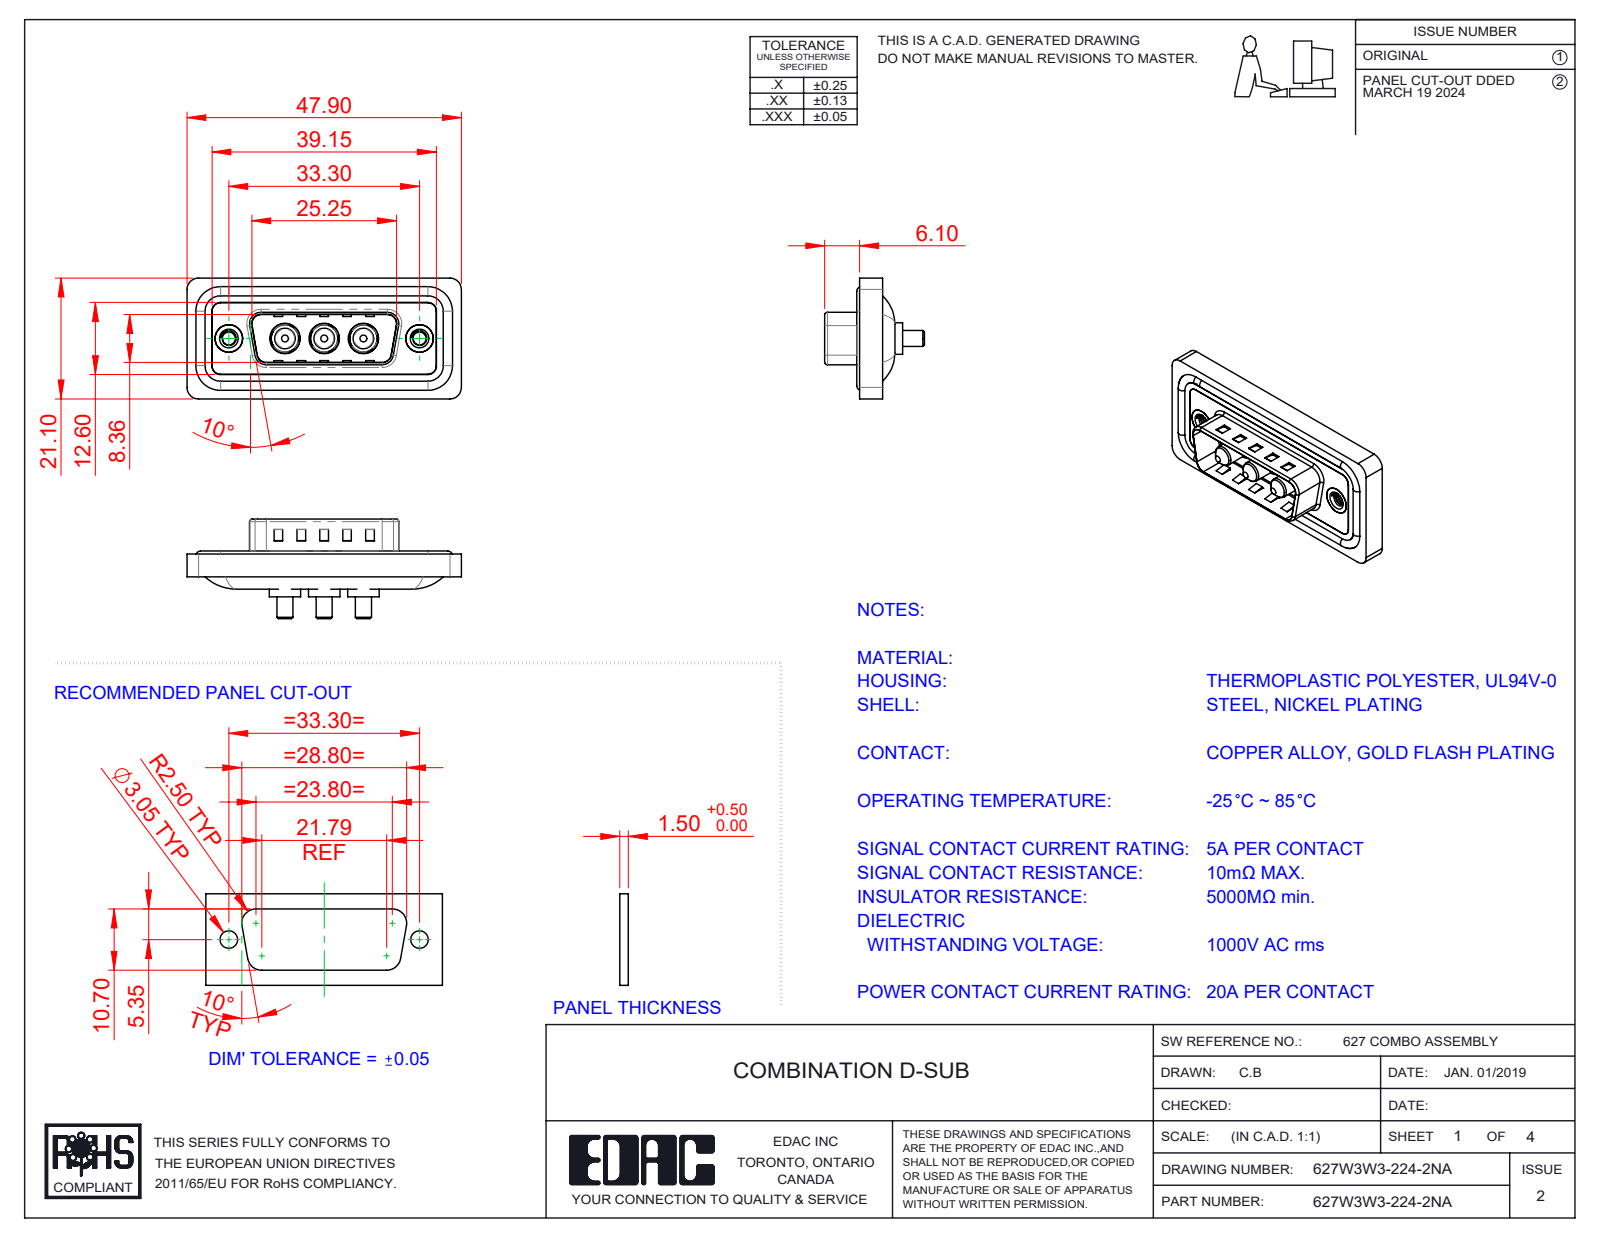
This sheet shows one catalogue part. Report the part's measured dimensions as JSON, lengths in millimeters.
{"part_name": "627W3W3-224-2NA; 627Combo Waterproof Housing_15 Contacts; Power Pin_20A S; 627Combo Shell Rear_15 Contacts (+3 more)", "step_written_by": "SolidWorks 2023 (CONFIG_CONTROL_DESIGN)", "units": "millimeters", "bodies": {"solids": 13, "faces": 562, "planar": 207, "cylindrical": 243, "other": 112}, "overall_size": [47.9, 21.1, 17.4], "volume_mm3": 5587, "surface_area_mm2": 8751, "round_holes": [[4.85, 3], [5.3, 3], [2.26, 2], [4, 2], [4.8, 2], [5, 2]], "round_bosses_or_shafts": [[1.6, 4], [5.5, 3], [5.2, 3], [4.75, 3], [3.75, 3], [3.6, 3], [2.8, 3], [4.9, 2]], "partial_cylinders_radius": [[1.5, 26], [2, 20], [0.5, 8], [1.6, 8], [0.25, 4], [0.6, 4], [0.65, 4], [0.9, 4]], "face_to_face_distances": [0.4, 1.1, 1.5, 0.5, 1.6, 3.1, 2.9, 4, 0.82, 9.58], "hole_center_spacings": [6.85, 9.8, 16.65, 23.5, 13.7, 33.3]}
